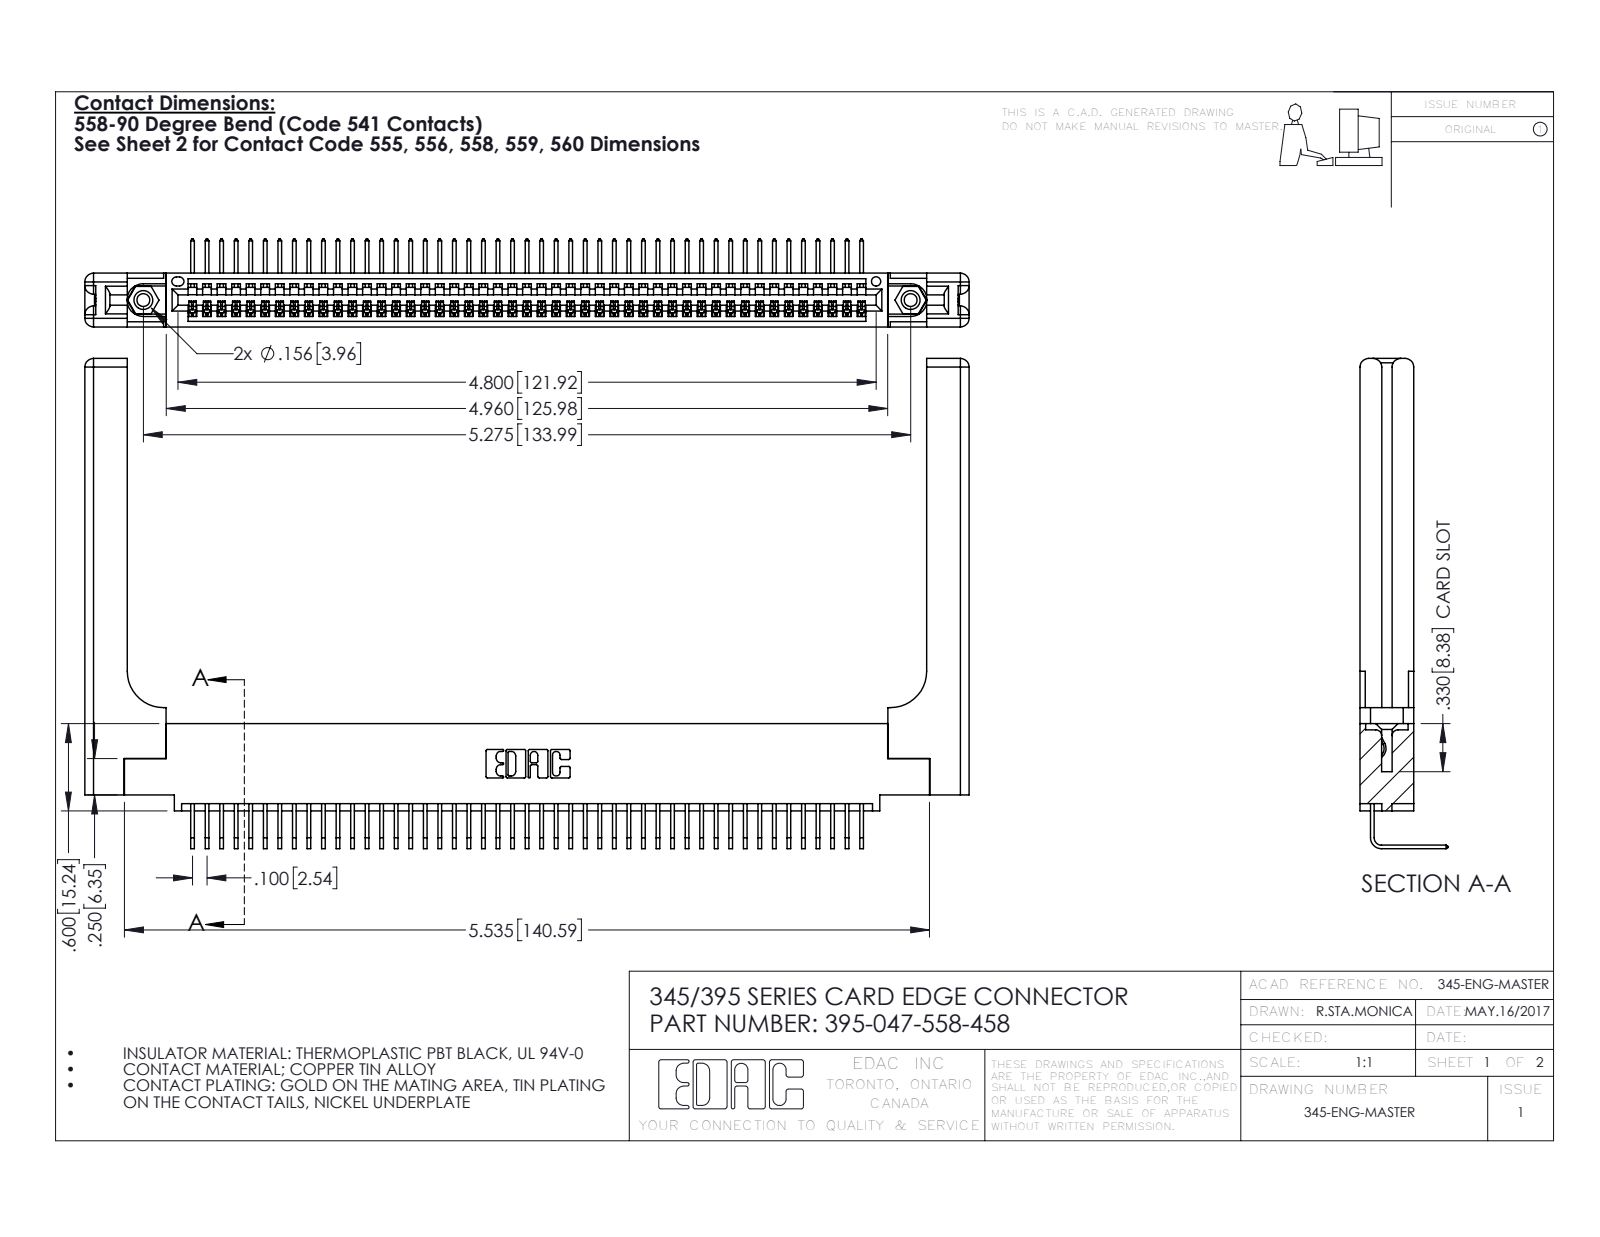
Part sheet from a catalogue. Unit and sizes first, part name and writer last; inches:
Units: inches
Overall size (bounding box): 6.079 × 3.369 × 0.605
Round holes (diameter × count): ⌀0.089 ×2, ⌀0.125 ×2, ⌀0.156 ×2, ⌀0.064 ×1
Round bosses / shafts (diameter × count): ⌀0.155 ×2
Partial cylindrical surfaces — rounded edges, fillets, slot ends (radius × count): R0.006 ×94, R0.01 ×22, R0.06 ×16, R0.007 ×6, R0.031 ×6, R0.026 ×3, R0.03 ×2, R0.031 ×2
Main face-to-face distances: 0.072, 0.37, 0.298, 0.098, 0.272, 0.025, 0.2, 0.225, 0.148, 0.15
Hole centre spacings: 0.27, 5.039, 5.275
Volume: 1.422 in³ · Surface area: 40.35 in²
Bodies: 52 solids, 3206 faces (2206 planar, 940 cylindrical, 60 other)
Part name (STEP PRODUCT): 395-047-558-458; 345-220-058_345-220-058; 345-292-001_558 Tail - 2; 345-250-001_345-250-001-102 (+1 more)
STEP written by: SolidWorks 2016 (CONFIG_CONTROL_DESIGN)
